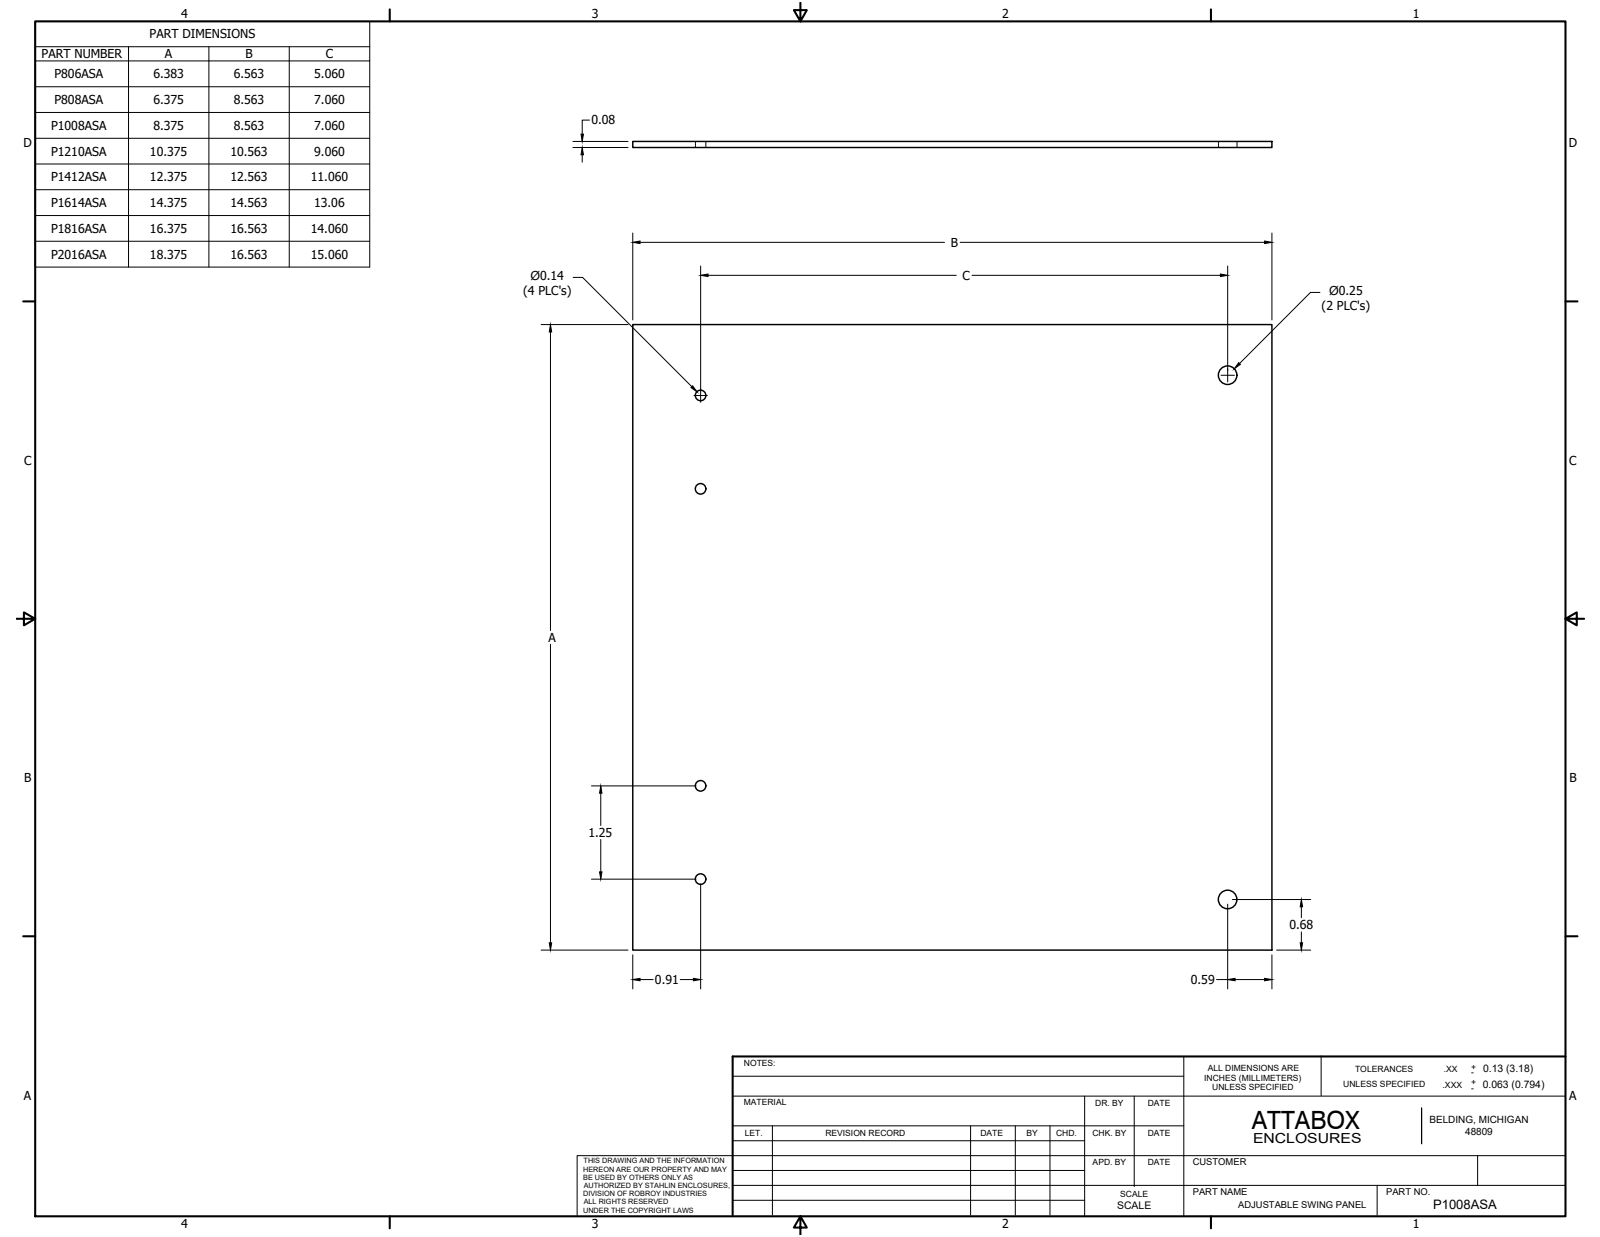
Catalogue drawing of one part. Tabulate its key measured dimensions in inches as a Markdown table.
| quantity | value |
| --- | --- |
| part name | P1008ASAL |
| STEP written by | Autodesk Inventor 11 (AUTOMOTIVE_DESIGN) |
| units | inches |
| bodies | 1 solid, 12 faces (6 planar, 6 cylindrical, 0 other) |
| overall size | 8.563 × 8.375 × 0.08 |
| volume | 5.724 in³ |
| surface area | 146.1 in² |
| round holes (diameter × count) | 0.14 × 4, 0.25 × 2 |
| main face-to-face distances | 0.08, 8.375, 8.562 |
| hole center spacings | 1.25, 5.226, 7.065, 7.222, 8.948, 9.766, 3.976, 6.476 |
